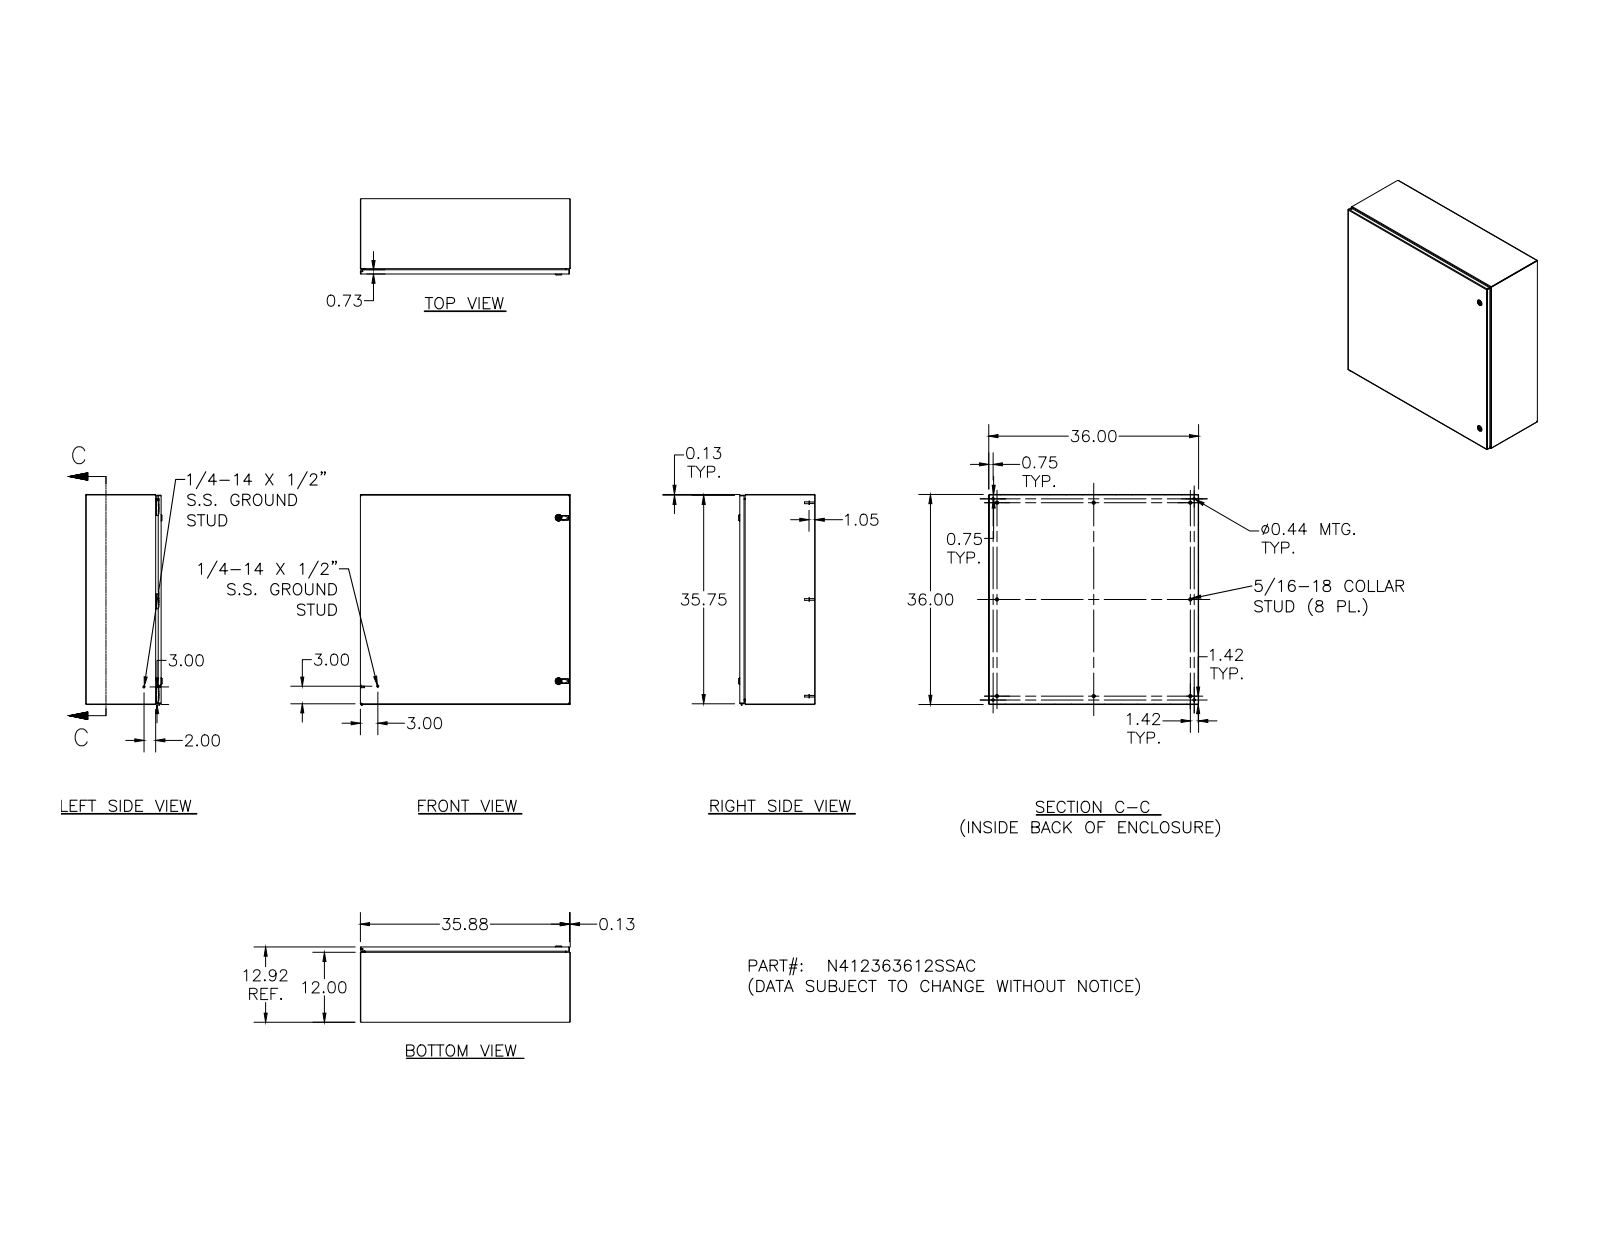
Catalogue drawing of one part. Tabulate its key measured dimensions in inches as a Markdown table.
| quantity | value |
| --- | --- |
| part name | N412SSACASSM3PCBTB; N412363612SSACBTB; N4123612SSACLS; N4123612SSACRS (+8 more) |
| STEP written by | Autodesk Inventor 2012 (AUTOMOTIVE_DESIGN) |
| units | inches |
| bodies | 53 solids, 2332 faces (905 planar, 862 cylindrical, 565 other) |
| overall size | 36 × 36 × 13.075 |
| volume | 340.9 in³ |
| surface area | 9 283 in² |
| round holes (diameter × count) | 0.093 × 6, 0.152 × 6, 0.167 × 6, 0.172 × 6, 0.187 × 6, 0.437 × 4, 0.156 × 3, 0.197 × 2, 0.315 × 2, 0.394 × 2, 0.402 × 2, 0.634 × 2 |
| round bosses / shafts (diameter × count) | 0.25 × 14, 0.563 × 8, 0.3 × 8, 0.275 × 8, 0.36 × 6, 0.32 × 6, 0.256 × 6, 0.164 × 6 |
| partial cylindrical surfaces (radius × count) | 0.012 × 54, 0.05 × 38, 0.031 × 32, 0.016 × 26, 0.125 × 24, 0.02 × 23, 0.105 × 18, 0.032 × 12 |
| main face-to-face distances | 0.074, 12.843, 35.926, 12.769, 12.917, 35.852, 36, 11.926, 0.917, 0.739 |
| hole center spacings | 16, 32, 16.008, 34.5, 0.5, 0.656, 0.66, 1.307 |
